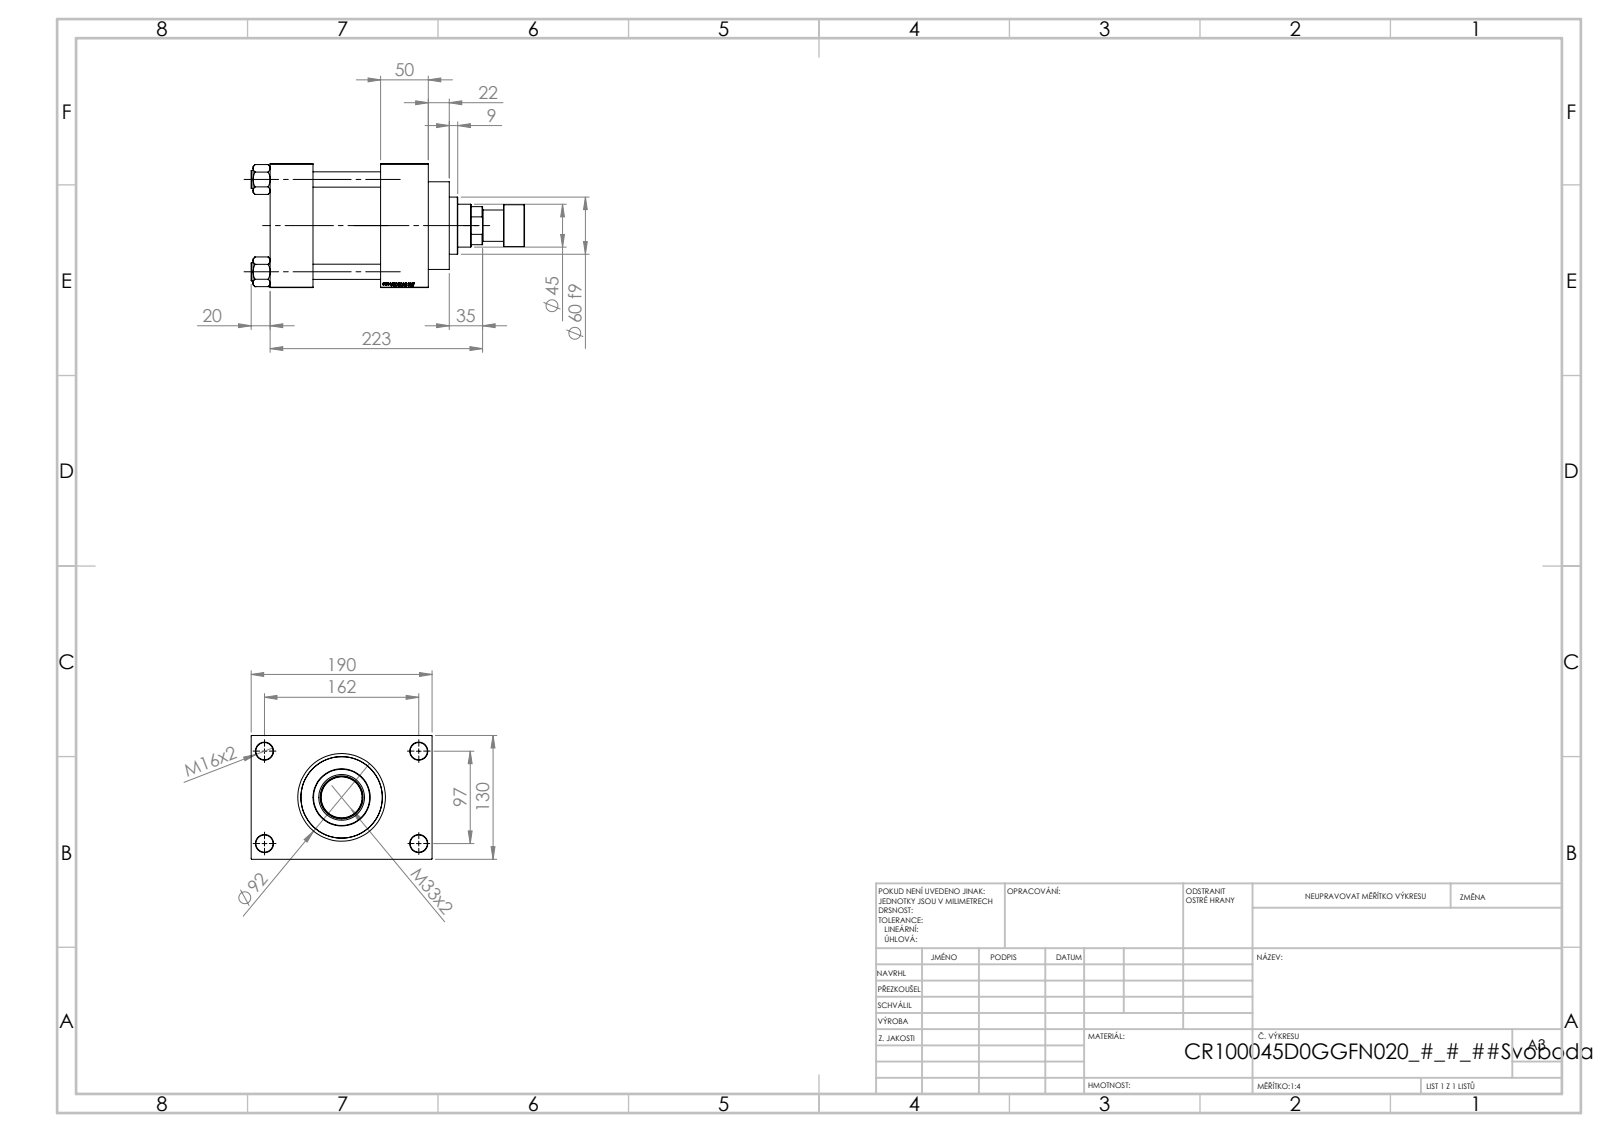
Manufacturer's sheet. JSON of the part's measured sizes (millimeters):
{"part_name": "V215CR_D_TYCINKA; V215CR_ROD_END_F; V215CR_D_Body; V215CR_VCP_D (+2 more)", "step_written_by": "SolidWorks 2019 (CONFIG_CONTROL_DESIGN)", "units": "millimeters", "bodies": {"solids": 12, "faces": 1165, "planar": 548, "cylindrical": 93, "other": 524}, "overall_size": [287, 190, 130], "volume_mm3": 2659000, "surface_area_mm2": 360772, "round_holes": [[16, 4], [18, 4], [7, 2], [26.44, 2], [35, 2], [31.5, 1], [45, 1], [48, 1], [76, 1], [85.5, 1], [100, 1]], "round_bosses_or_shafts": [[19, 4], [106, 1], [92, 1], [60, 1], [44, 1], [33, 1]], "face_to_face_distances": [130, 116, 45, 71, 166, 121, 50, 30, 160, 70], "hole_center_spacings": [32.55, 68.52, 94.41, 96.9, 102.27, 129.45, 161.73, 97]}
